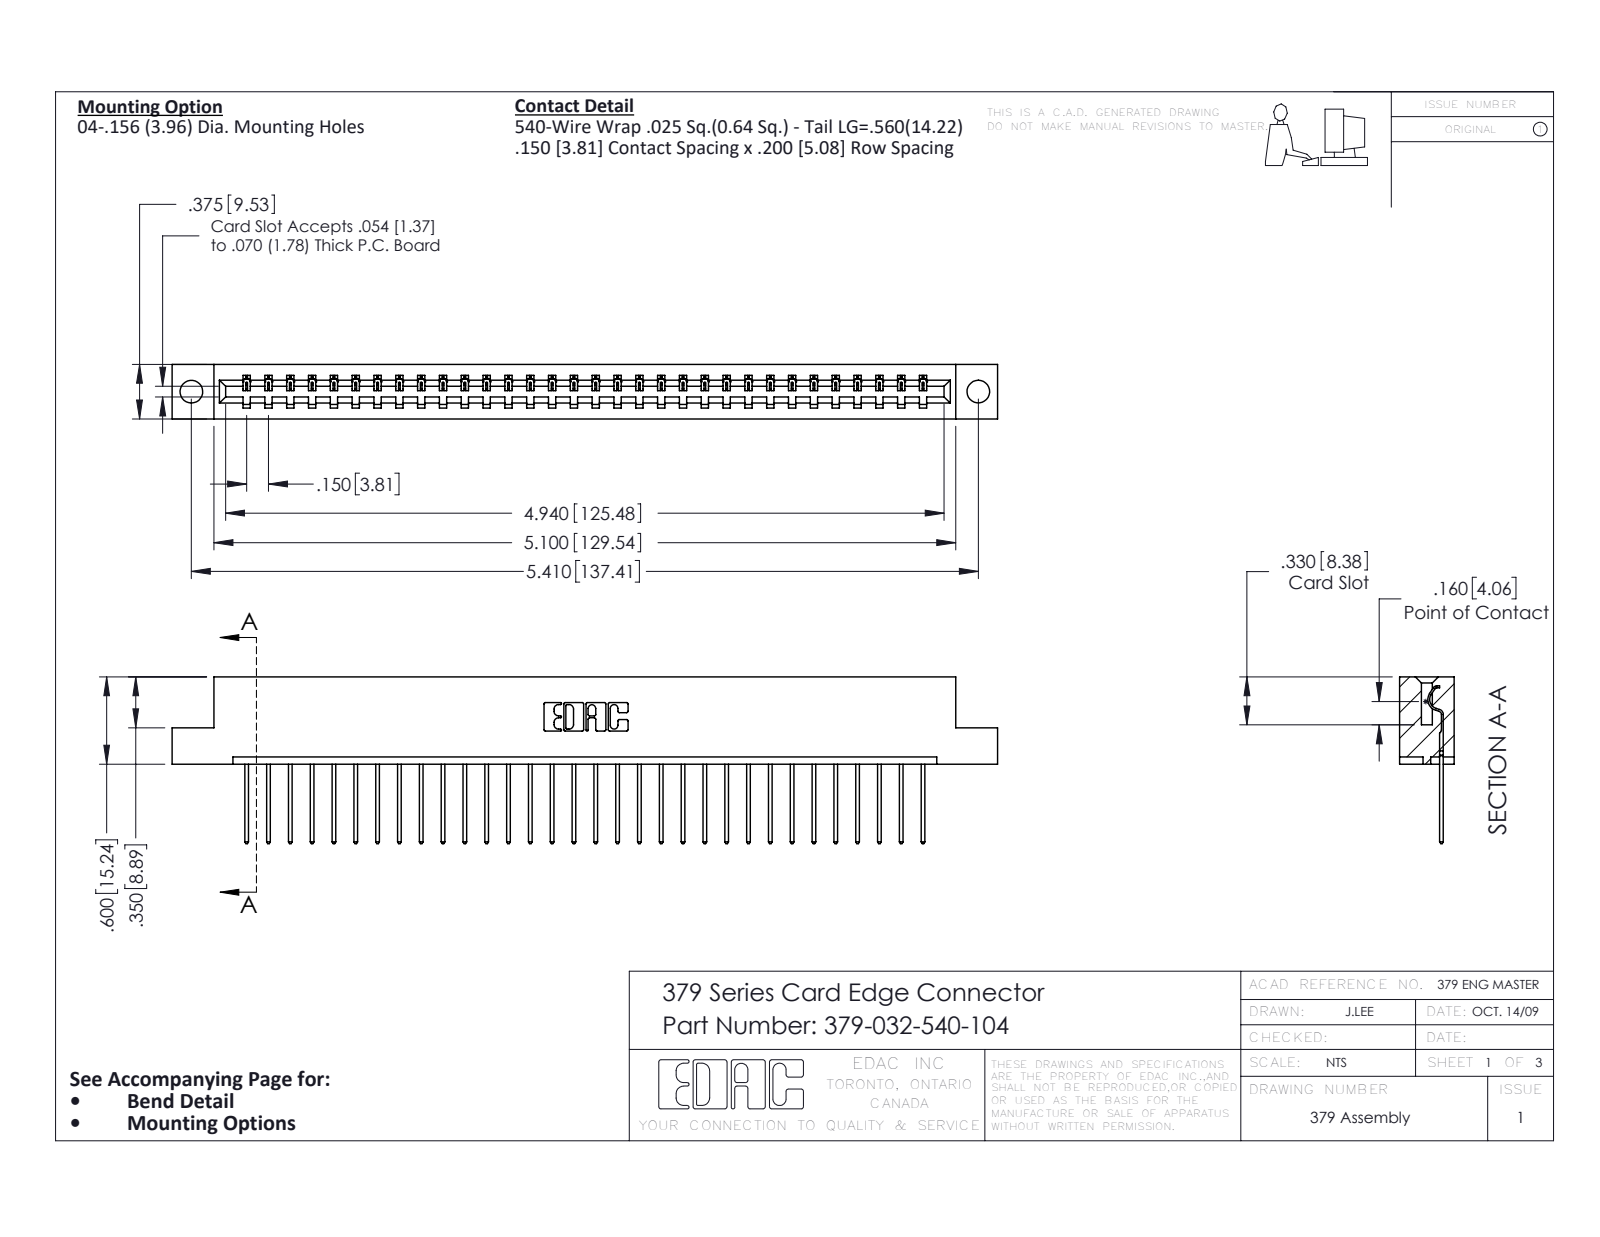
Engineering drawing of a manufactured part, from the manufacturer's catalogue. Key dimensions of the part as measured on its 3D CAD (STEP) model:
Part name (STEP PRODUCT): 379-032-540-104; 345-292-001_345-293-140; 379 Part_Flush - .156 Dia - TH
STEP written by: SolidWorks 2016 (CONFIG_CONTROL_DESIGN)
Units: inches
Bodies: 33 solids, 1970 faces (1414 planar, 556 cylindrical, 0 other)
Overall size (bounding box): 5.675 × 1.147 × 0.375
Volume: 0.914 in³ · Surface area: 23.86 in²
Round holes (diameter × count): ⌀0.156 ×2
Partial cylindrical surfaces — rounded edges, fillets, slot ends (radius × count): R0.006 ×64, R0.01 ×64, R0.01 ×22, R0.007 ×6, R0.031 ×6, R0.026 ×3, R0.014 ×1, R0.022 ×1
Main face-to-face distances: 0.3, 0.075, 0.375, 0.225, 0.275, 0.1, 0.025, 0.2, 0.6, 0.55
Hole centre spacings: 5.41
